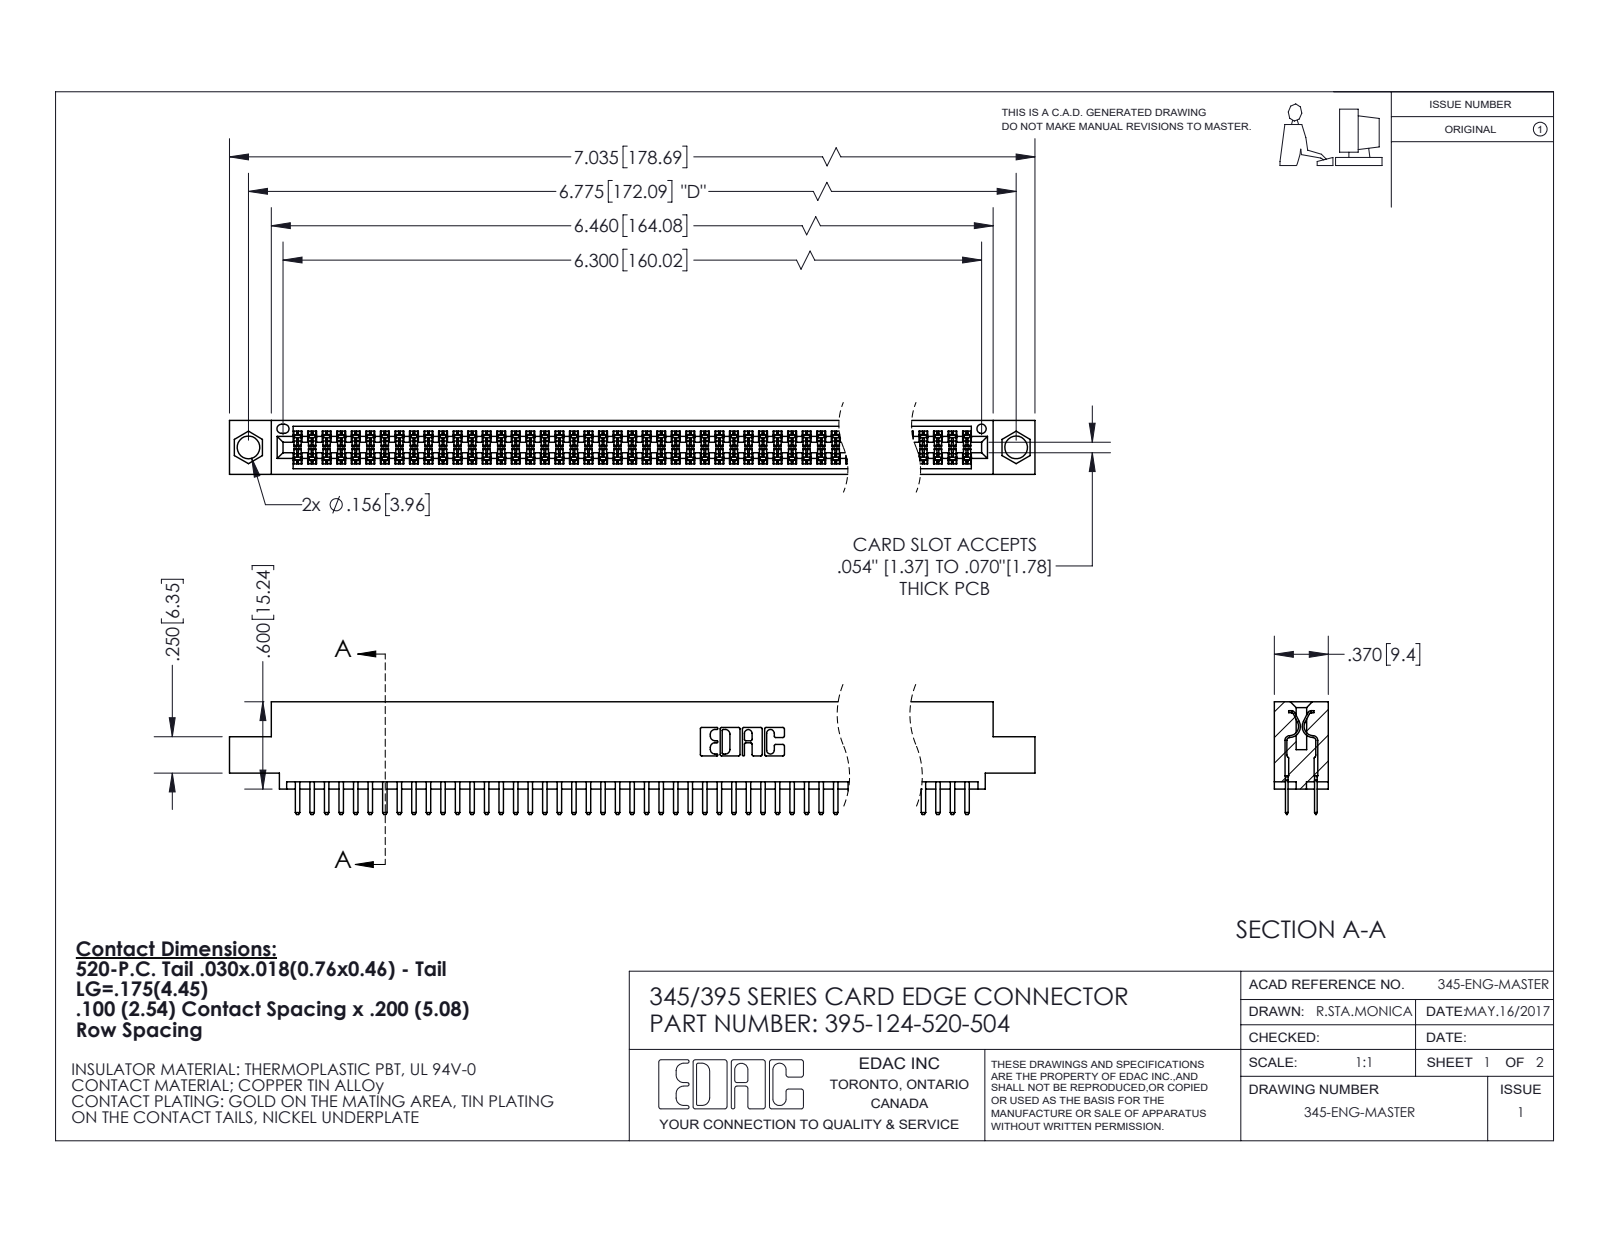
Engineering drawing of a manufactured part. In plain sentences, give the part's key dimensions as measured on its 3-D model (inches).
The part is named "395-124-520-504; 345-292-001_345-293-120; 345 Part_0.110 Offset - 0.156 Dia-TI". Its 3-D file was written by "SolidWorks 2020 (CONFIG_CONTROL_DESIGN)". It is 125 solids with 6840 faces: 4438 planar, 2402 cylindrical and 0 other. Overall it measures 7.035 by 0.775 by 0.37 inches. Its volume is 1.056 cubic inches and its surface area 39.99 square inches. Round holes: 2 of diameter 0.156, 1 of diameter 0.064. Partial cylindrical surfaces (rounded edges, fillets, slot ends): 186 of radius 0.006, 128 of radius 0.01, 22 of radius 0.01, 6 of radius 0.007, 6 of radius 0.031, 3 of radius 0.026, 2 of radius 0.014, 2 of radius 0.019. The main face-to-face distances are 0.298, 0.072, 0.2, 0.37, 0.098, 0.272, 0.025, 0.225, 0.022, 0.072. The hole center spacings are 0.27, 6.539, 6.775.
